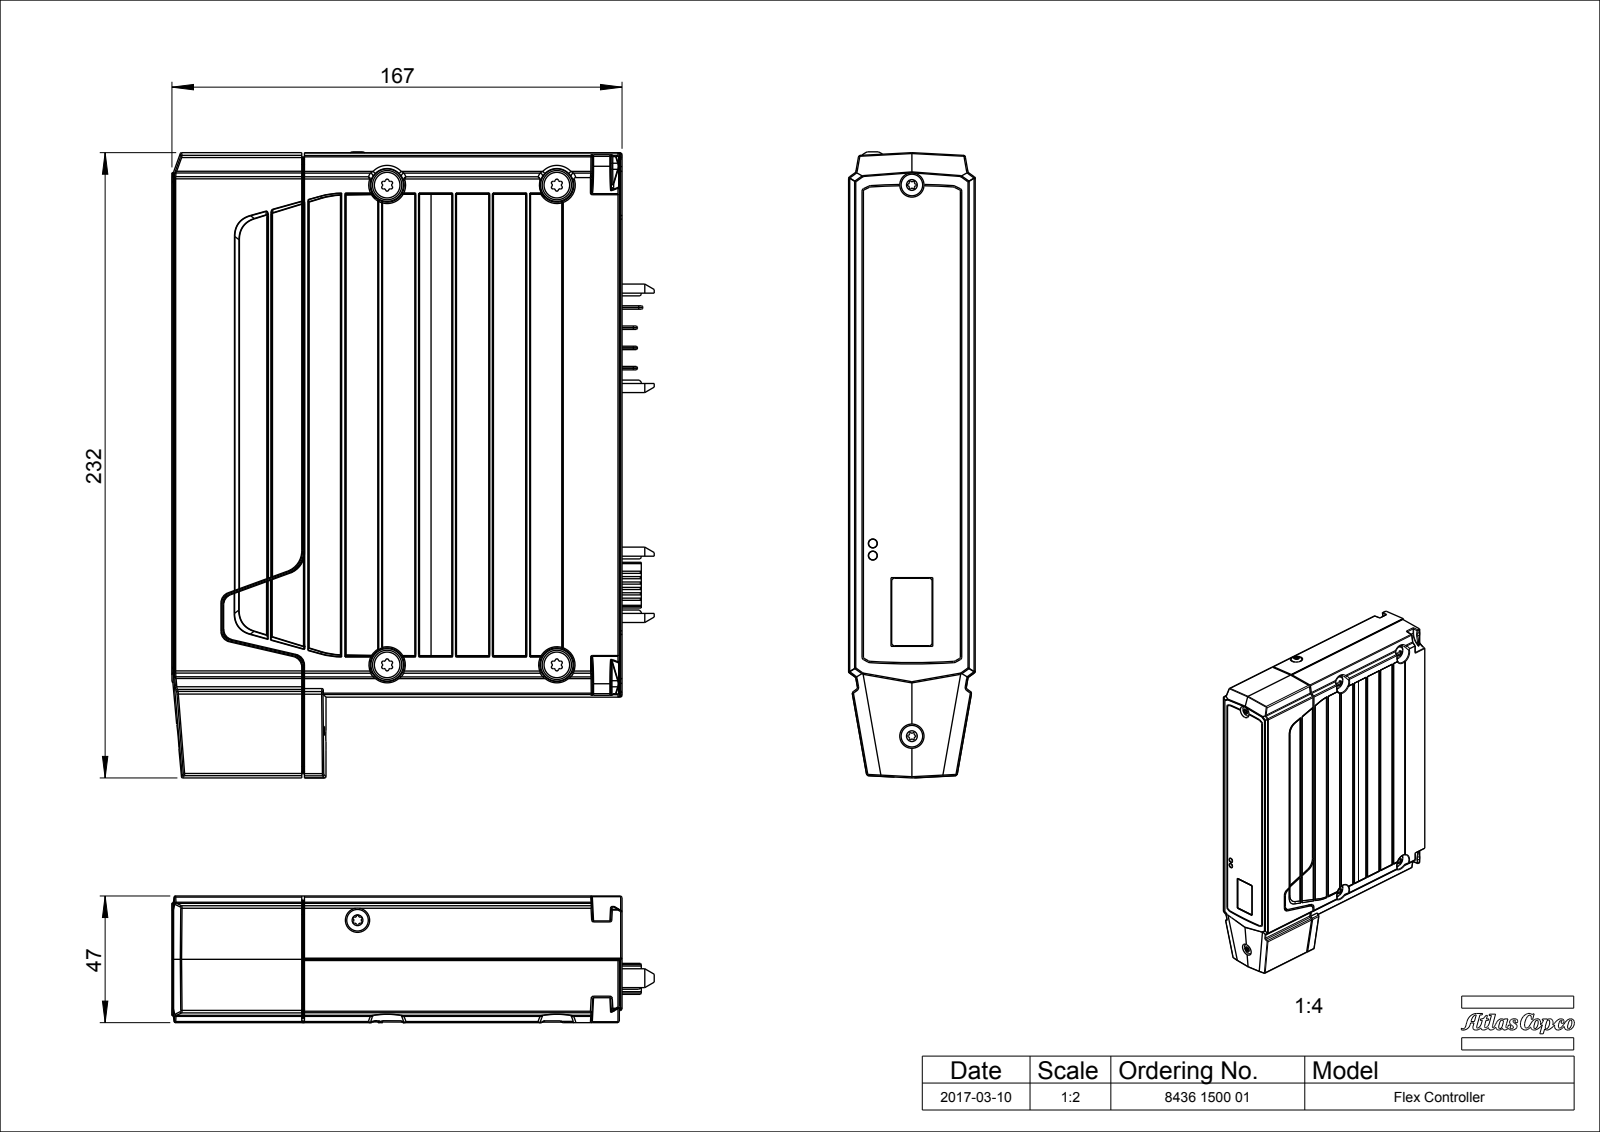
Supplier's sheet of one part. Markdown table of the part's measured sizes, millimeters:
| quantity | value |
| --- | --- |
| part name | 4222186912; 4222184120_DESIGN; J8064D628ANL; TYCO_292303-1 (+8 more) |
| STEP written by | CREO PARAMETRIC BY PTC INC, 2020281 (CONFIG_CONTROL_DESIGN) |
| units | millimeters |
| bodies | 63 solids, 13993 faces (9493 planar, 2759 cylindrical, 1741 other) |
| overall size | 232.3 × 179.05 × 47 |
| volume | 1 468 000 mm³ |
| surface area | 430 644 mm² |
| round holes (diameter × count) | 1.4 × 22, 1.45 × 22, 3.3 × 13, 0.92 × 8, 2.5 × 8, 1.3 × 6, 3.2 × 5, 0.8 × 4, 1 × 4, 2.3 × 4, 2.6 × 4, 5.5 × 4 |
| round bosses / shafts (diameter × count) | 1.7 × 22, 0.46 × 16, 5.6 × 13, 3 × 13, 8 × 9, 4 × 7, 2 × 7, 1 × 7 |
| partial cylindrical surfaces (radius × count) | 1 × 227, 0.5 × 200, 0.3 × 170, 0.2 × 134, 0.1 × 110, 0.29 × 78, 0.51 × 78, 0.58 × 48 |
| main face-to-face distances | 1.6, 26.3, 11.5, 3, 35.5, 32.5, 8.5, 10, 21.5, 14 |
| hole center spacings | 3.5, 7, 10.5, 14, 17.5, 21, 40.39, 43.89 |
